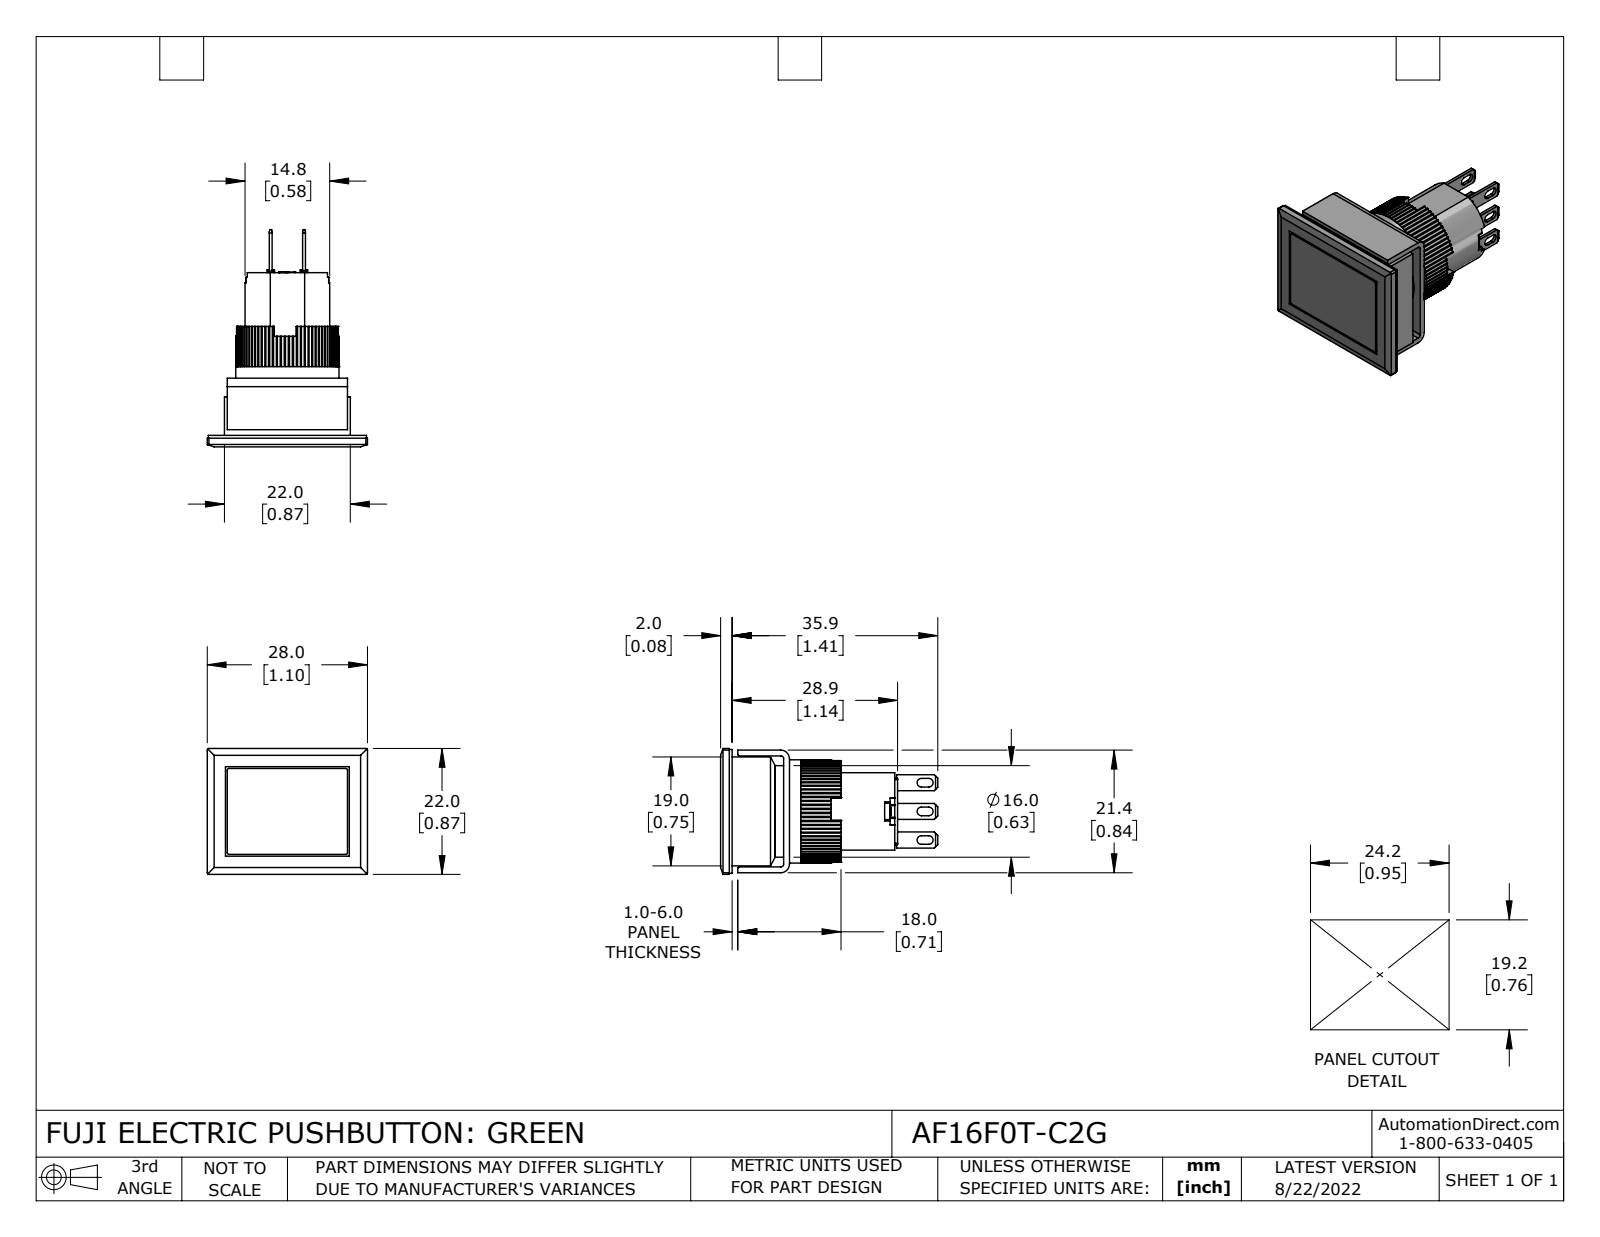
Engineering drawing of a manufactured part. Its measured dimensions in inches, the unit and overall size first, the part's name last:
Units: inches
Overall size (bounding box): 1.492 × 1.102 × 0.866
Round holes (diameter × count): ⌀0.039 ×1, ⌀0.709 ×1
Round bosses / shafts (diameter × count): ⌀0.63 ×1, ⌀0.583 ×1
Partial cylindrical surfaces — rounded edges, fillets, slot ends (radius × count): R0.01 ×80, R0.008 ×12, R0.012 ×8, R0.03 ×6, R0.02 ×2, R0.059 ×2
Main face-to-face distances: 0.374, 0.059, 0.02, 0.142, 0.039, 0.315, 0.232, 0.083, 0.079, 0.756
Volume: 0.541 in³ · Surface area: 11.85 in²
Bodies: 12 solids, 798 faces (620 planar, 176 cylindrical, 2 other)
Part name (STEP PRODUCT): AF16F0T-C2G
STEP written by: SolidWorks 2021 (CONFIG_CONTROL_DESIGN)
